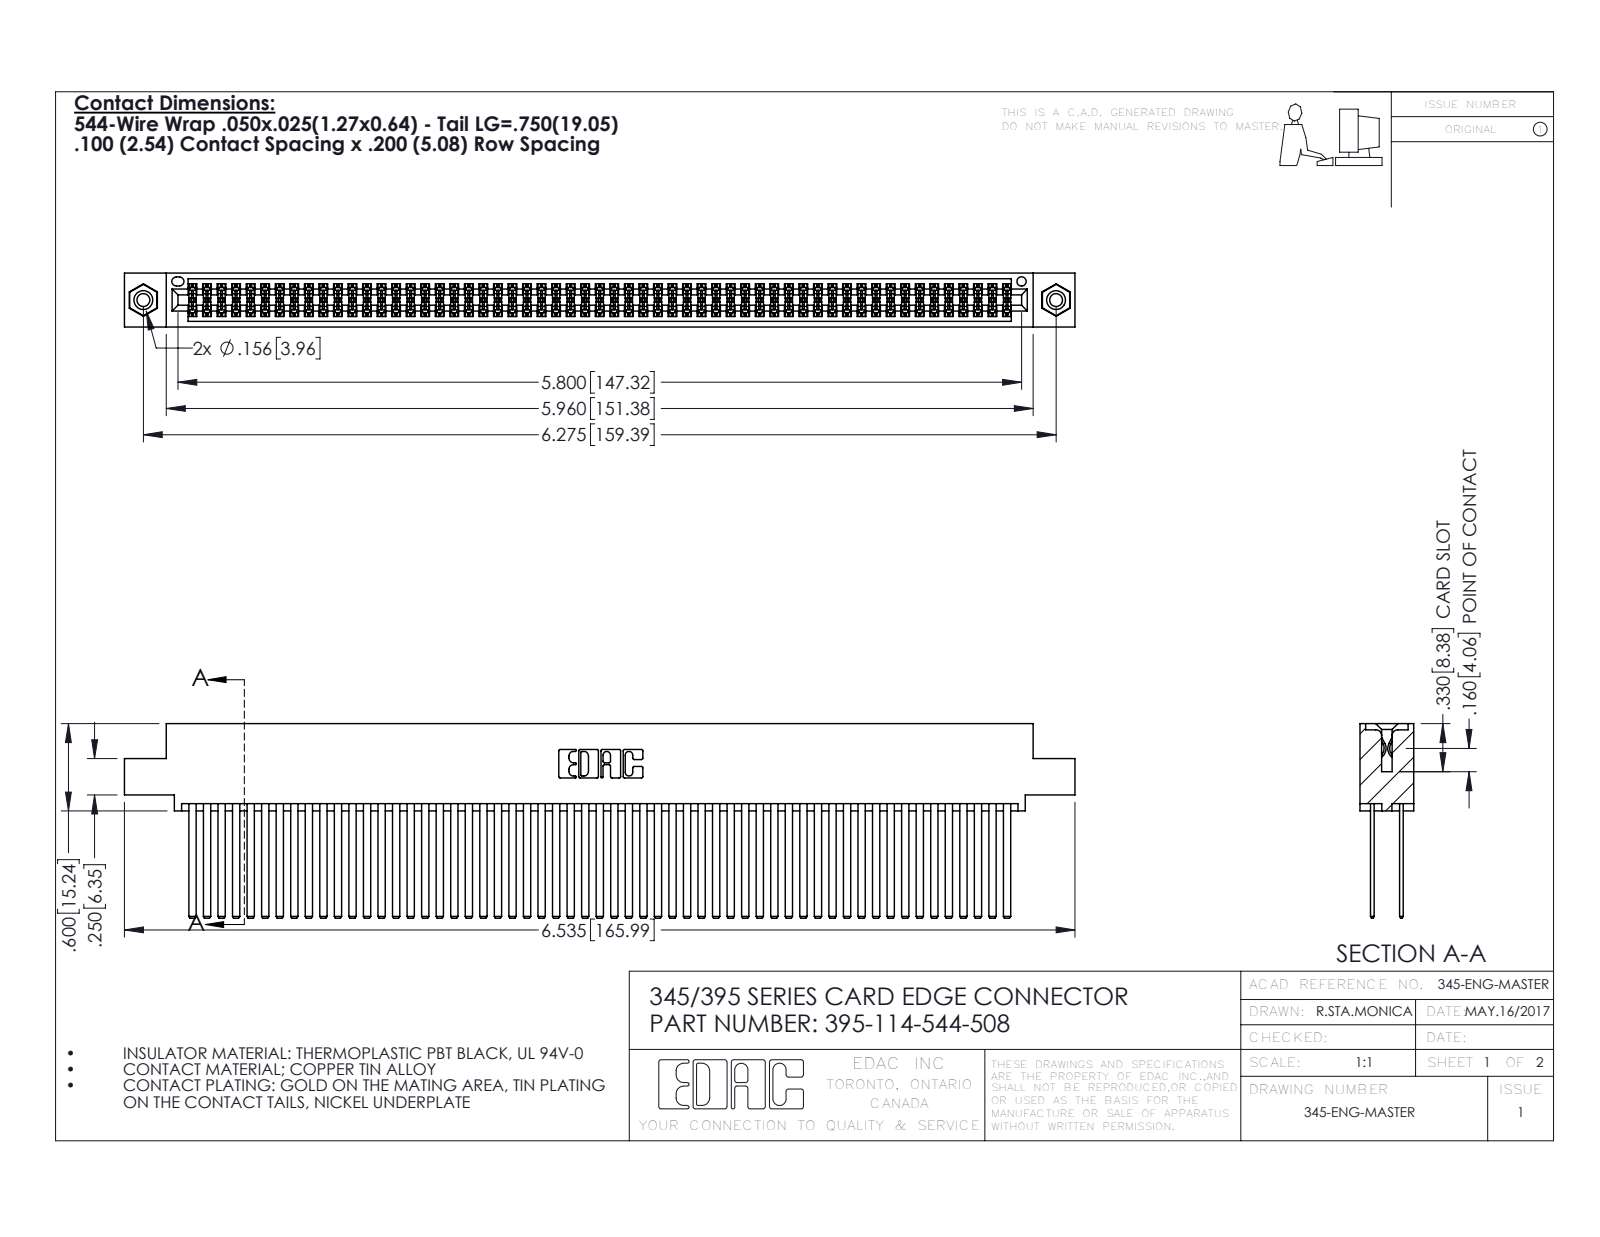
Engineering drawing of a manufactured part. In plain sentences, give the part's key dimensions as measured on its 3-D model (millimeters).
The part is named "395-114-544-508; 345-250-001_345-250-003-102; 345 Part_0.110 Offset - 0.156 Dia-TI; 345-292-001_345-293-144". Its 3-D file was written by "SolidWorks 2016 (CONFIG_CONTROL_DESIGN)". It is 117 solids with 5206 faces: 3422 planar, 1768 cylindrical and 16 other. Overall it measures 166 by 34 by 9.4 millimeters. Its volume is 17 780 cubic millimeters and its surface area 31 370 square millimeters. Round holes: 2 of diameter 2.3, 2 of diameter 3.2, 2 of diameter 4, 1 of diameter 1.6. Round bosses or shafts: 2 of diameter 3.9. Partial cylindrical surfaces (rounded edges, fillets, slot ends): 171 of radius 0.2, 22 of radius 0.3, 6 of radius 0.2, 6 of radius 0.8, 3 of radius 0.7, 2 of radius 0.4, 2 of radius 0.5, 2 of radius 0.6. The main face-to-face distances are 5.1, 0.6, 1.8, 2.5, 6.9, 7.6, 5.7, 4.4, 9.4, 1.3. The hole center spacings are 6.9, 153.4, 159.4.
